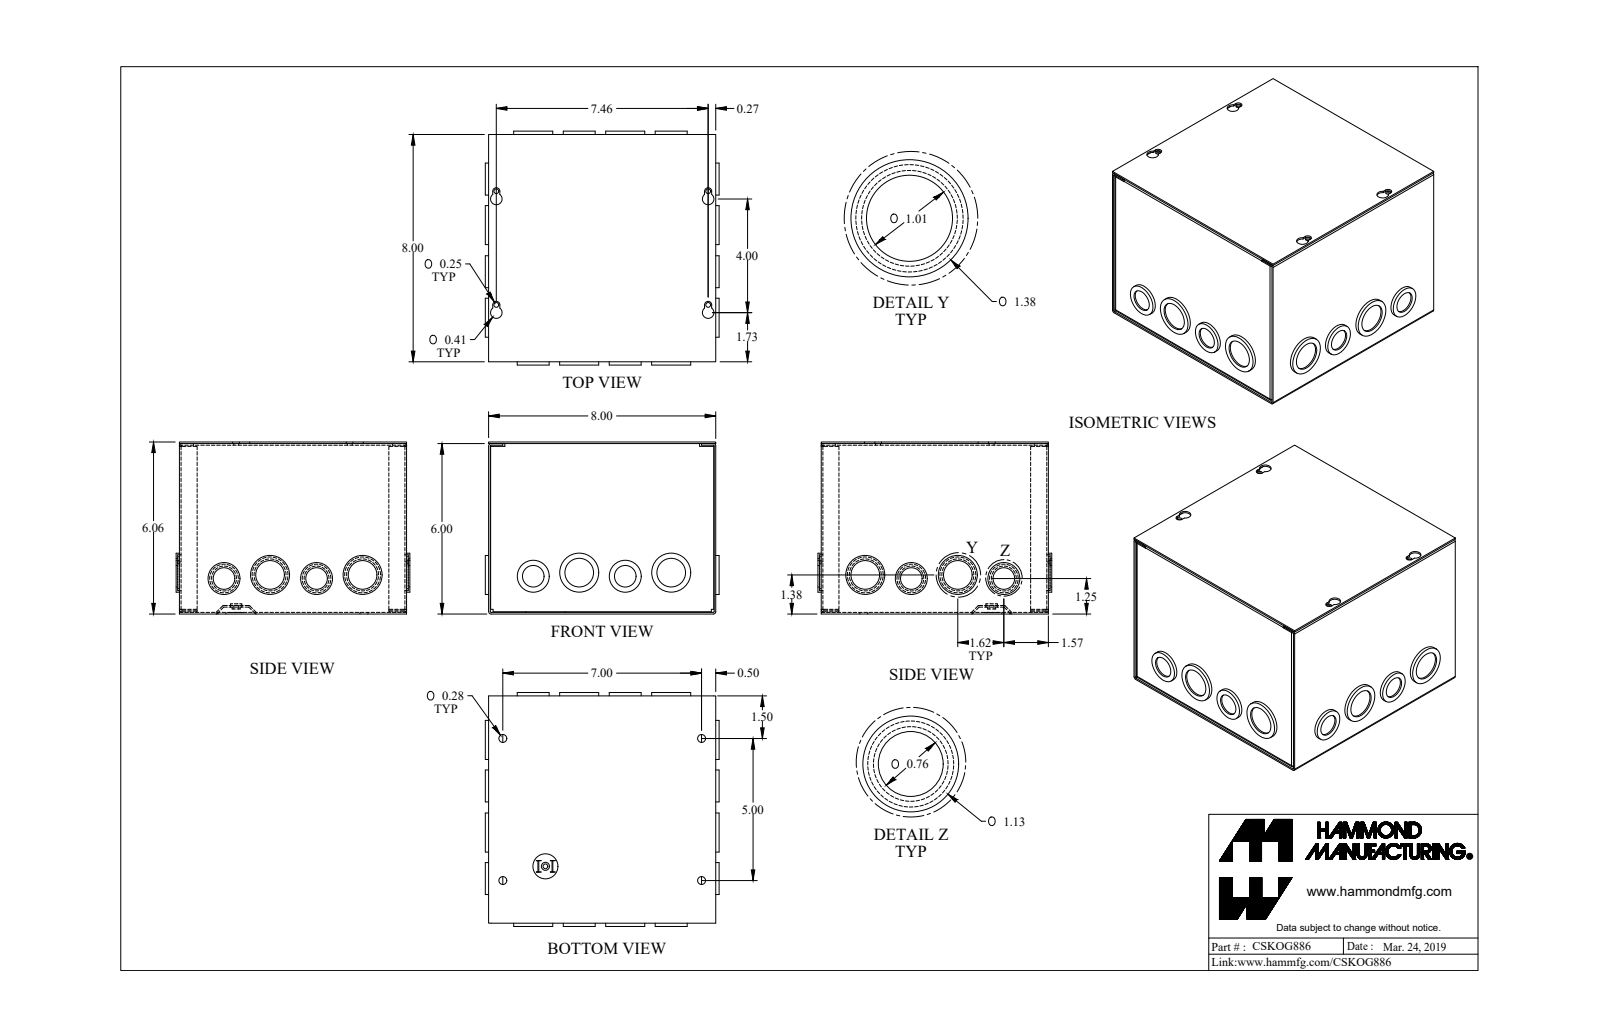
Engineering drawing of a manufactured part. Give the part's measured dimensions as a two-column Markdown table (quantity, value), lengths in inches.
| quantity | value |
| --- | --- |
| part name | CSKOG886_Default |
| STEP written by | SolidWorks 2019 (CONFIG_CONTROL_DESIGN) |
| units | inches |
| bodies | 4 solids, 397 faces (189 planar, 200 cylindrical, 8 other) |
| overall size | 8.234 × 8.234 × 6.057 |
| volume | 20.41 in³ |
| surface area | 725.6 in² |
| round holes (diameter × count) | 1.011 × 12, 0.761 × 6, 1.261 × 6, 0.17 × 5, 0.281 × 4, 0.5 × 1 |
| round bosses / shafts (diameter × count) | 1.125 × 7, 1.375 × 6, 1.125 × 6, 0.875 × 5, 0.875 × 3, 0.492 × 1, 0.284 × 1 |
| partial cylindrical surfaces (radius × count) | 0.029 × 12, 0.086 × 12, 0.057 × 8, 0.125 × 4, 0.203 × 4 |
| main face-to-face distances | 0.057, 7.943, 6, 8, 7.886, 5.943, 6.057, 7.873, 0.07, 0.114 |
| hole center spacings | 1.625, 0.125, 0.55, 1.62, 3.24, 3.242, 4.506, 7.247 |
